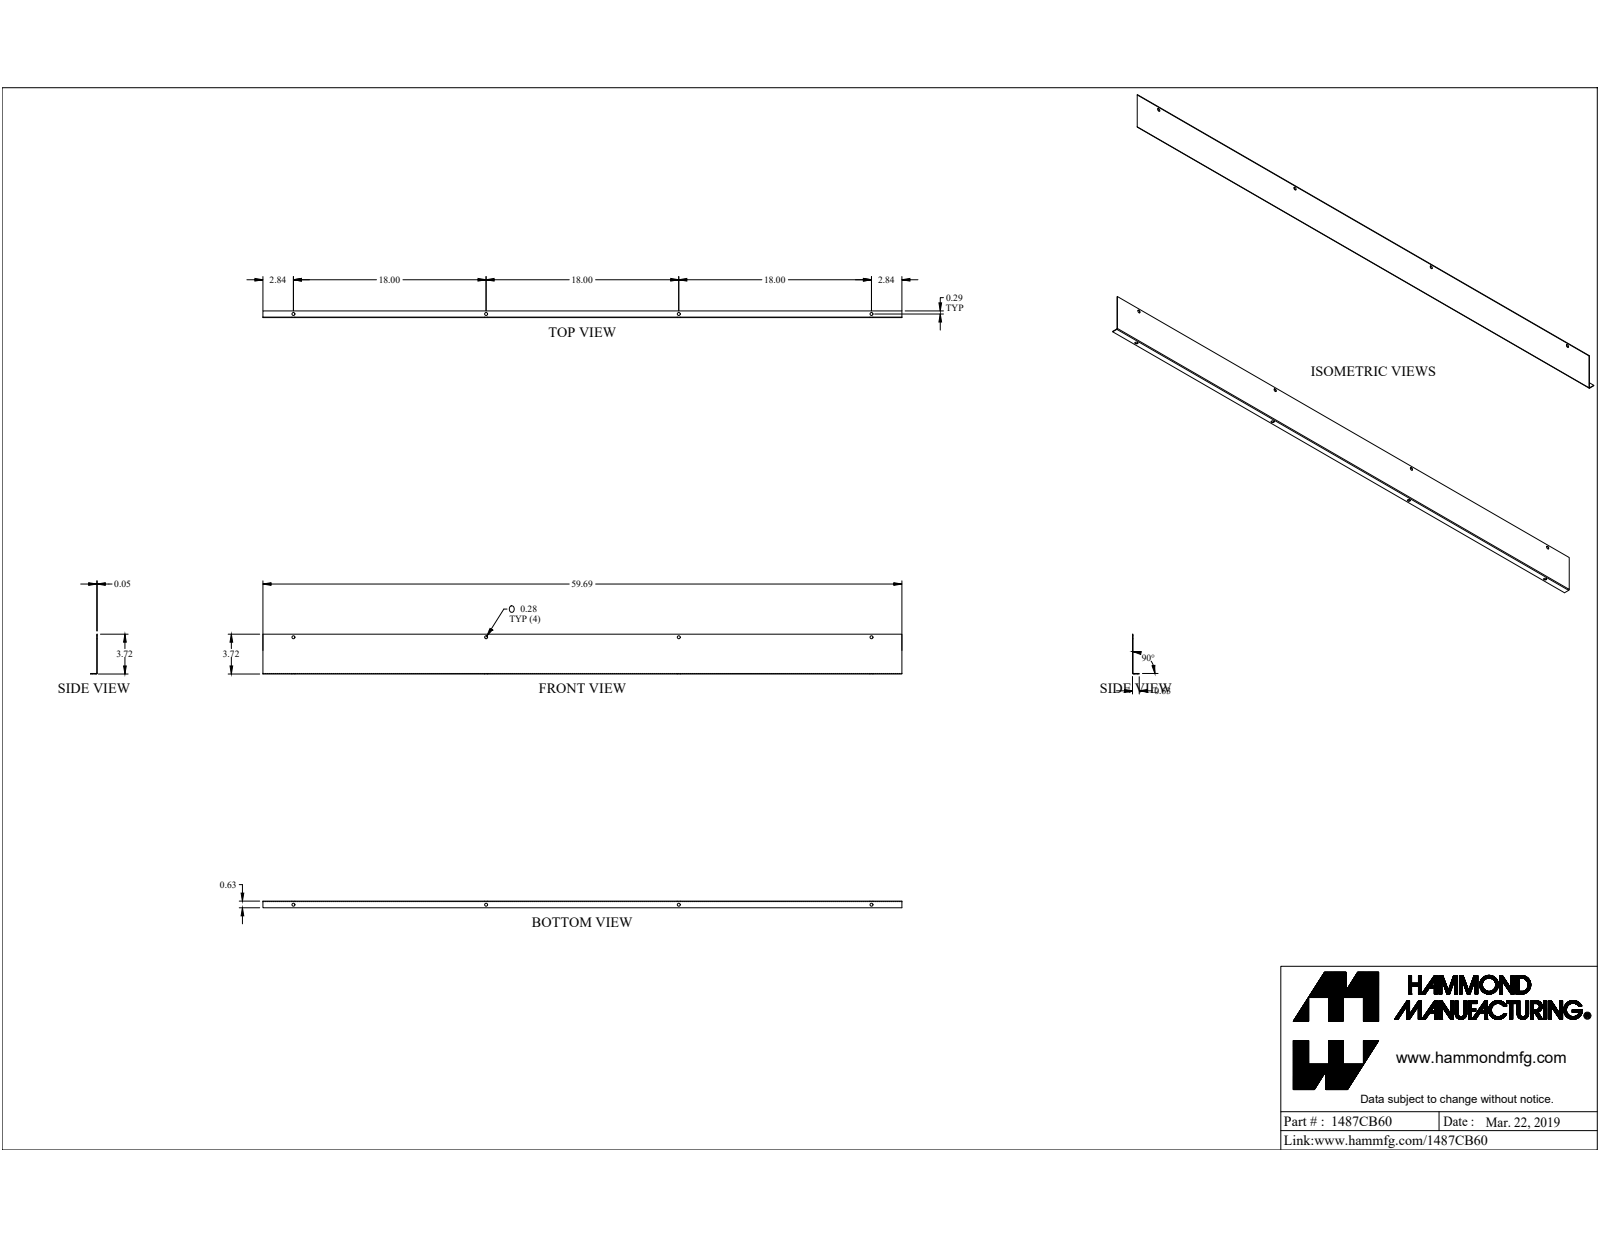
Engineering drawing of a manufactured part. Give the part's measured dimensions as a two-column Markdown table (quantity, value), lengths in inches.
| quantity | value |
| --- | --- |
| part name | 1487CB60 |
| STEP written by | SolidWorks 2019 (CONFIG_CONTROL_DESIGN) |
| units | inches |
| bodies | 4 solids, 63 faces (33 planar, 15 cylindrical, 15 other) |
| overall size | 59.687 × 4.218 × 0.844 |
| volume | 12.29 in³ |
| surface area | 517.7 in² |
| round holes (diameter × count) | 0.281 × 8, 0.25 × 1, 0.26 × 1 |
| round bosses / shafts (diameter × count) | 0.51 × 1, 0.438 × 1, 0.224 × 1 |
| partial cylindrical surfaces (radius × count) | 0.024 × 1, 0.072 × 1 |
| main face-to-face distances | 0.048, 0.625, 0.577, 3.718, 3.67, 59.687, 0.03, 0.018, 0.595, 0.438 |
| hole center spacings | 18, 36, 9.006, 27.002, 54, 9.631, 9.632, 27.217 |
